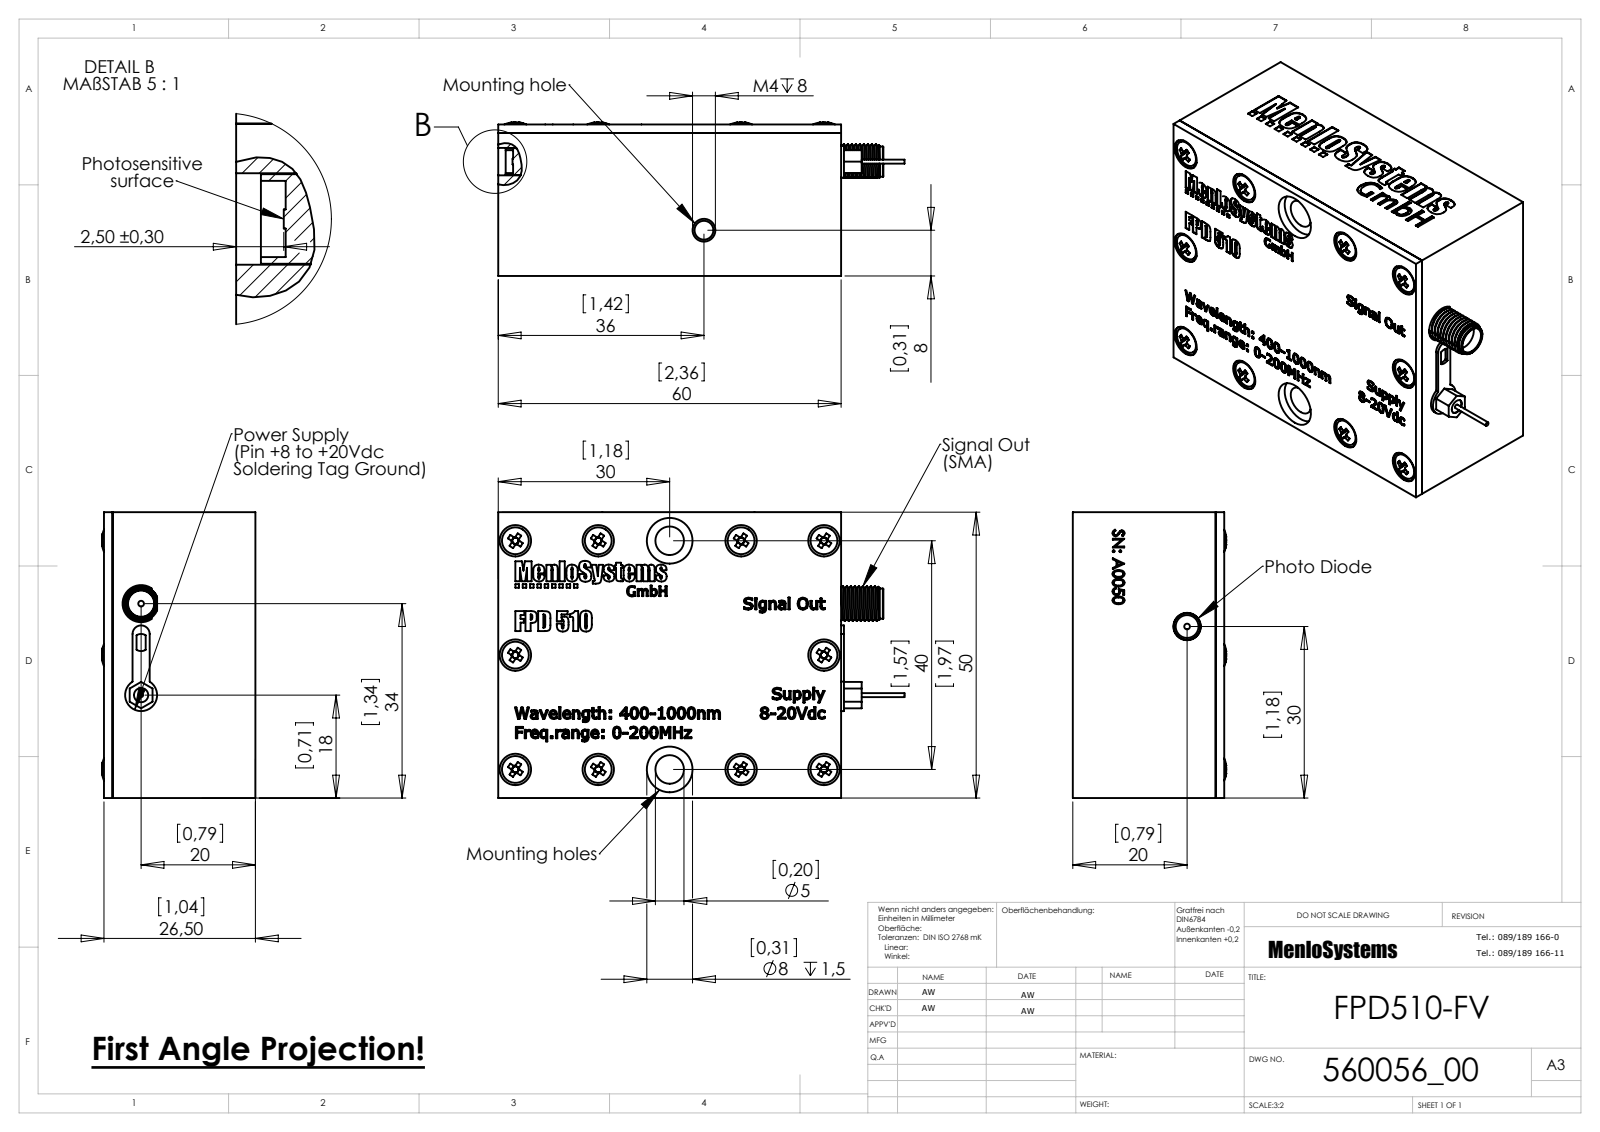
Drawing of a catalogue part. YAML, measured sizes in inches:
part_name: "600470_1_FPD510-FV; SW3dPS-sma bulkhead straight jack_echt; 600238_FPD510F; Countersunk Raised Head Cross Recess Screw_DIN_ISO 7047 - M2.5 x 6 - Z --- 6N (+4 more)"
step_written_by: "SolidWorks 2007 (AUTOMOTIVE_DESIGN)"
units: inches
bodies: {solids: 17, faces: 2451, planar: 1317, cylindrical: 172, other: 962}
overall_size: [2.799, 1.969, 1.057]
volume: 4.763
surface_area: 34.83
round_holes:
  - {diameter: 0.098, count: 11}
  - {diameter: 0.081, count: 10}
  - {diameter: 0.217, count: 10}
  - {diameter: 0.157, count: 2}
  - {diameter: 0.197, count: 2}
  - {diameter: 0.315, count: 2}
  - {diameter: 0.039, count: 1}
  - {diameter: 0.118, count: 1}
  - {diameter: 0.13, count: 1}
  - {diameter: 0.181, count: 1}
  - {diameter: 0.189, count: 1}
round_bosses_or_shafts:
  - {diameter: 0.185, count: 11}
  - {diameter: 0.02, count: 6}
  - {diameter: 0.24, count: 1}
  - {diameter: 0.22, count: 1}
  - {diameter: 0.213, count: 1}
  - {diameter: 0.208, count: 1}
  - {diameter: 0.039, count: 1}
  - {diameter: 0.028, count: 1}
partial_cylinders:
  - {radius: 0.039, count: 4}
  - {radius: 0.079, count: 4}
  - {radius: 0.059, count: 2}
  - {radius: 0.08, count: 2}
  - {radius: 0.128, count: 1}
face_to_face_distances: [0.984, 0.059, 1.043, 0.079, 0.02, 0.965, 1.969, 2.362, 1.965, 0.394]
hole_center_spacings: [1.575, 0.492, 0.571, 0.787, 0.972, 1.063, 1.323, 1.555]
